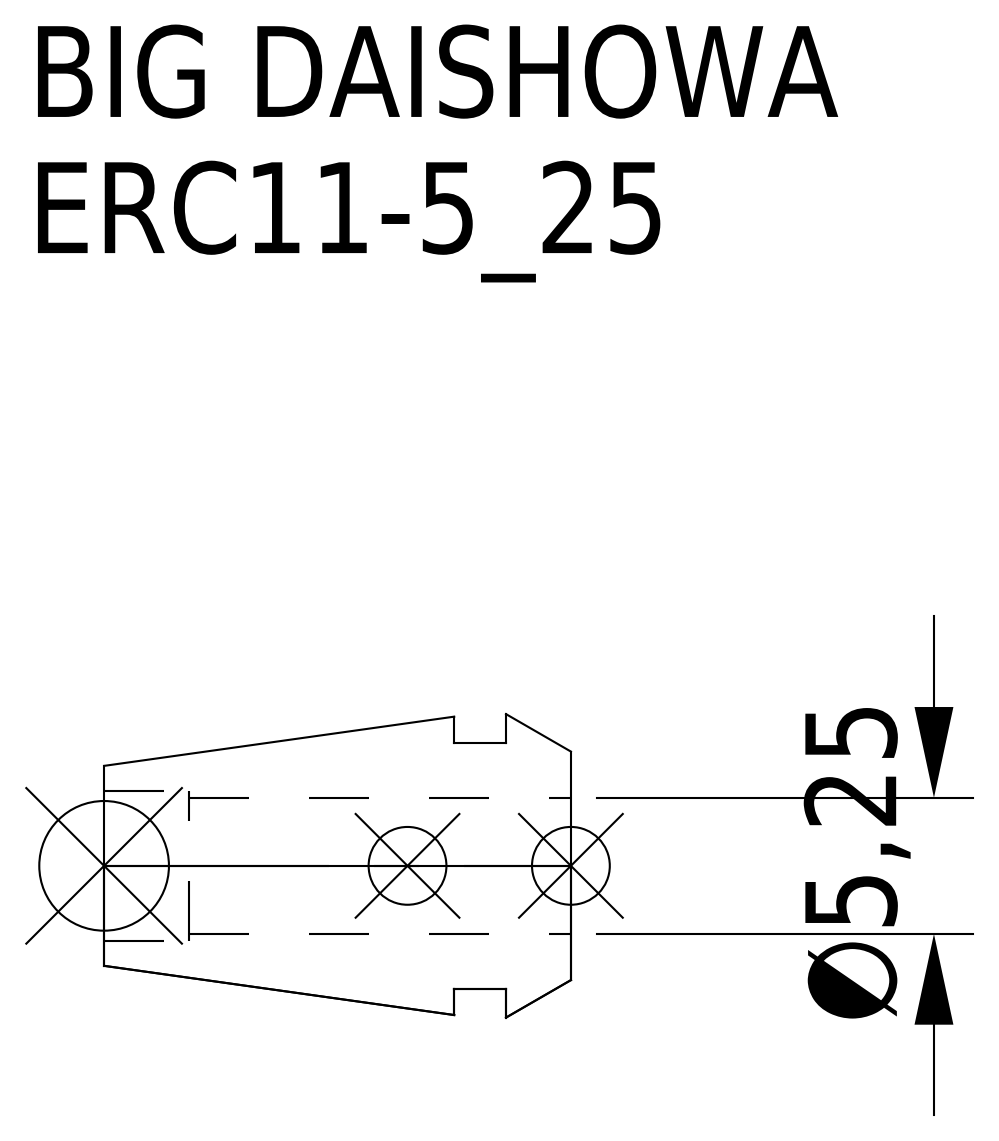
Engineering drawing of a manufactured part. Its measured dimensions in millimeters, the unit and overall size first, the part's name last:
Units: millimetres
Overall size (bounding box): 18 × 11.7 × 11.7
Round holes (diameter × count): ⌀5.25 ×1, ⌀5.8 ×1
Round bosses / shafts (diameter × count): ⌀9.5 ×1
Main face-to-face distances: 2.5, 4.5, 2, 18, 15.5, 13.5, 14.72, 12.22, 10.22, 3.28
Volume: 936 mm³ · Surface area: 1 001 mm²
Bodies: 1 solid, 15 faces (5 planar, 6 cylindrical, 4 other)
Part name (STEP PRODUCT): ERC11-5_25
STEP written by: CREO PARAMETRIC BY PTC INC, 2016380 (AUTOMOTIVE_DESIGN)
